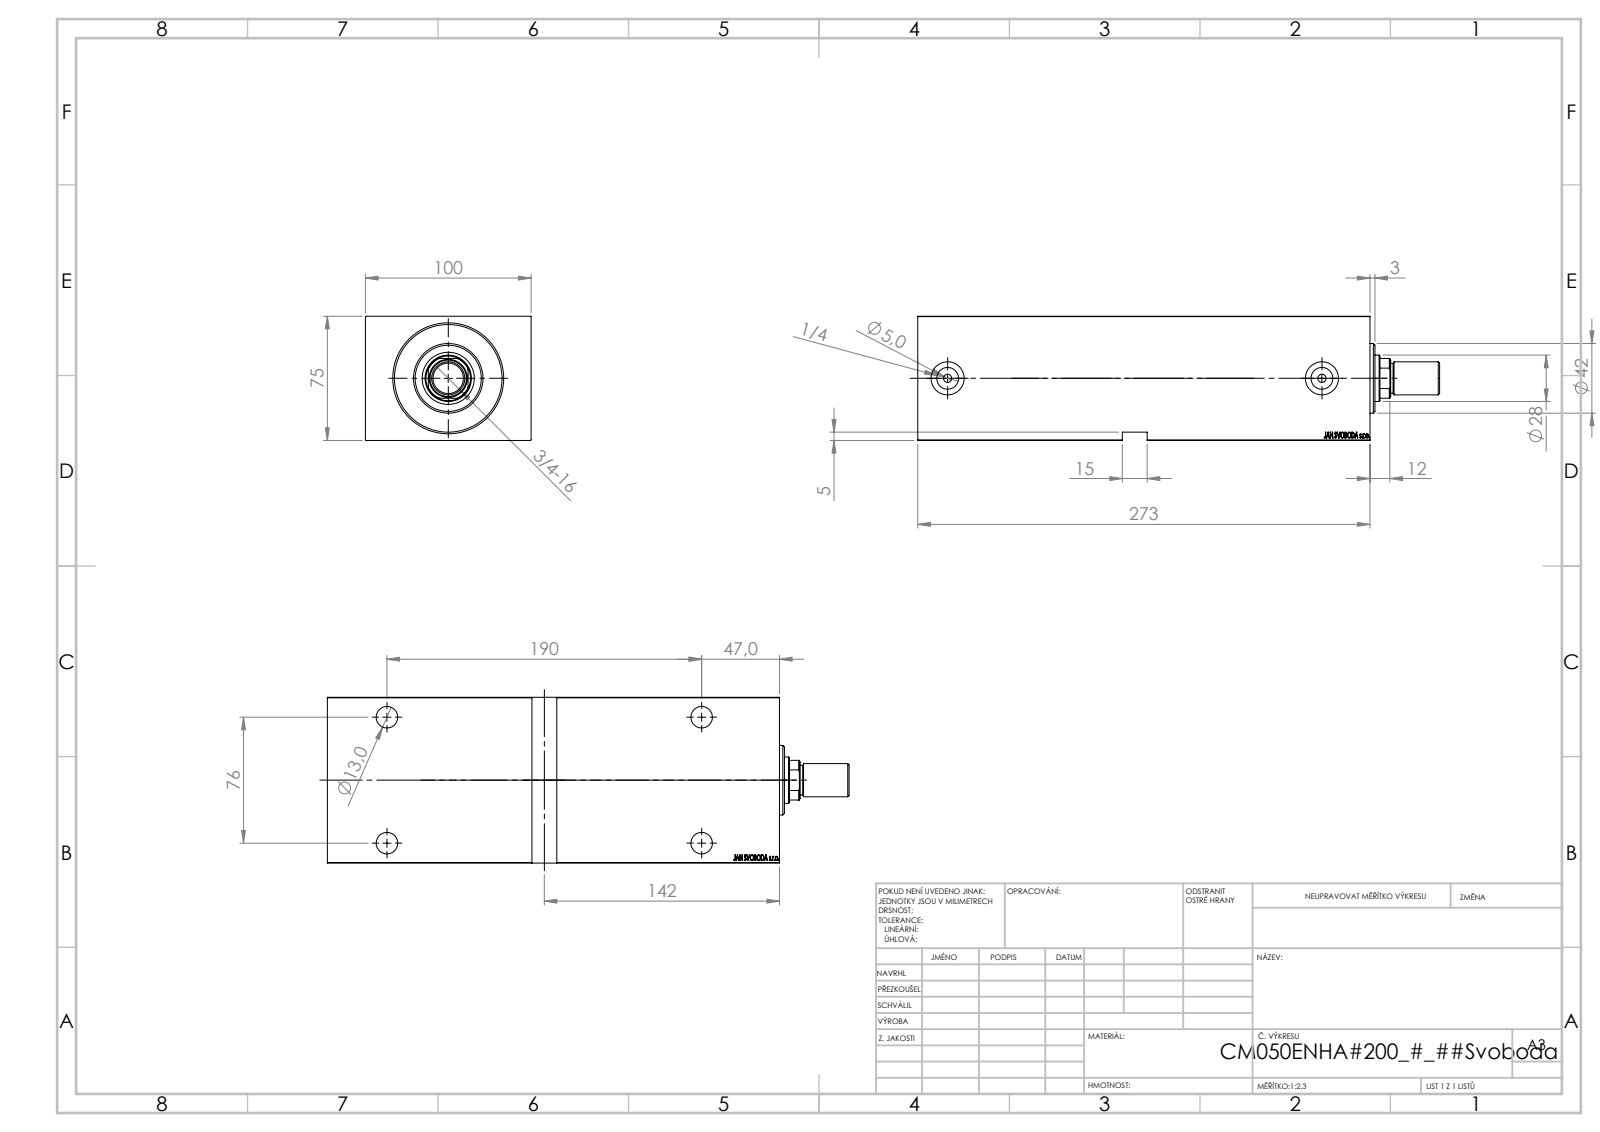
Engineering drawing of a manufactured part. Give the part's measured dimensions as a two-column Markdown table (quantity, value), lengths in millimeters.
| quantity | value |
| --- | --- |
| part name | V450CM_MALE_METRIC; V450CM_E_VCP; V450CM_VC_B; V450CM_E_Body |
| STEP written by | SolidWorks 2019 (CONFIG_CONTROL_DESIGN) |
| units | millimeters |
| bodies | 4 solids, 870 faces (414 planar, 56 cylindrical, 400 other) |
| overall size | 315 × 100 × 75 |
| volume | 1 732 000 mm³ |
| surface area | 211 981 mm² |
| round holes (diameter × count) | 13 × 4, 19 × 4, 5 × 2, 13.16 × 2, 20 × 2, 18.5 × 1, 28 × 1, 31.5 × 1, 50 × 1, 65 × 1 |
| round bosses / shafts (diameter × count) | 52 × 1, 42 × 1, 20 × 1, 18 × 1 |
| partial cylindrical surfaces (radius × count) | 13.5 × 1 |
| main face-to-face distances | 75, 100, 273, 5, 14, 259, 254, 268, 47, 256.4 |
| hole center spacings | 76, 190, 204.64, 226 |
